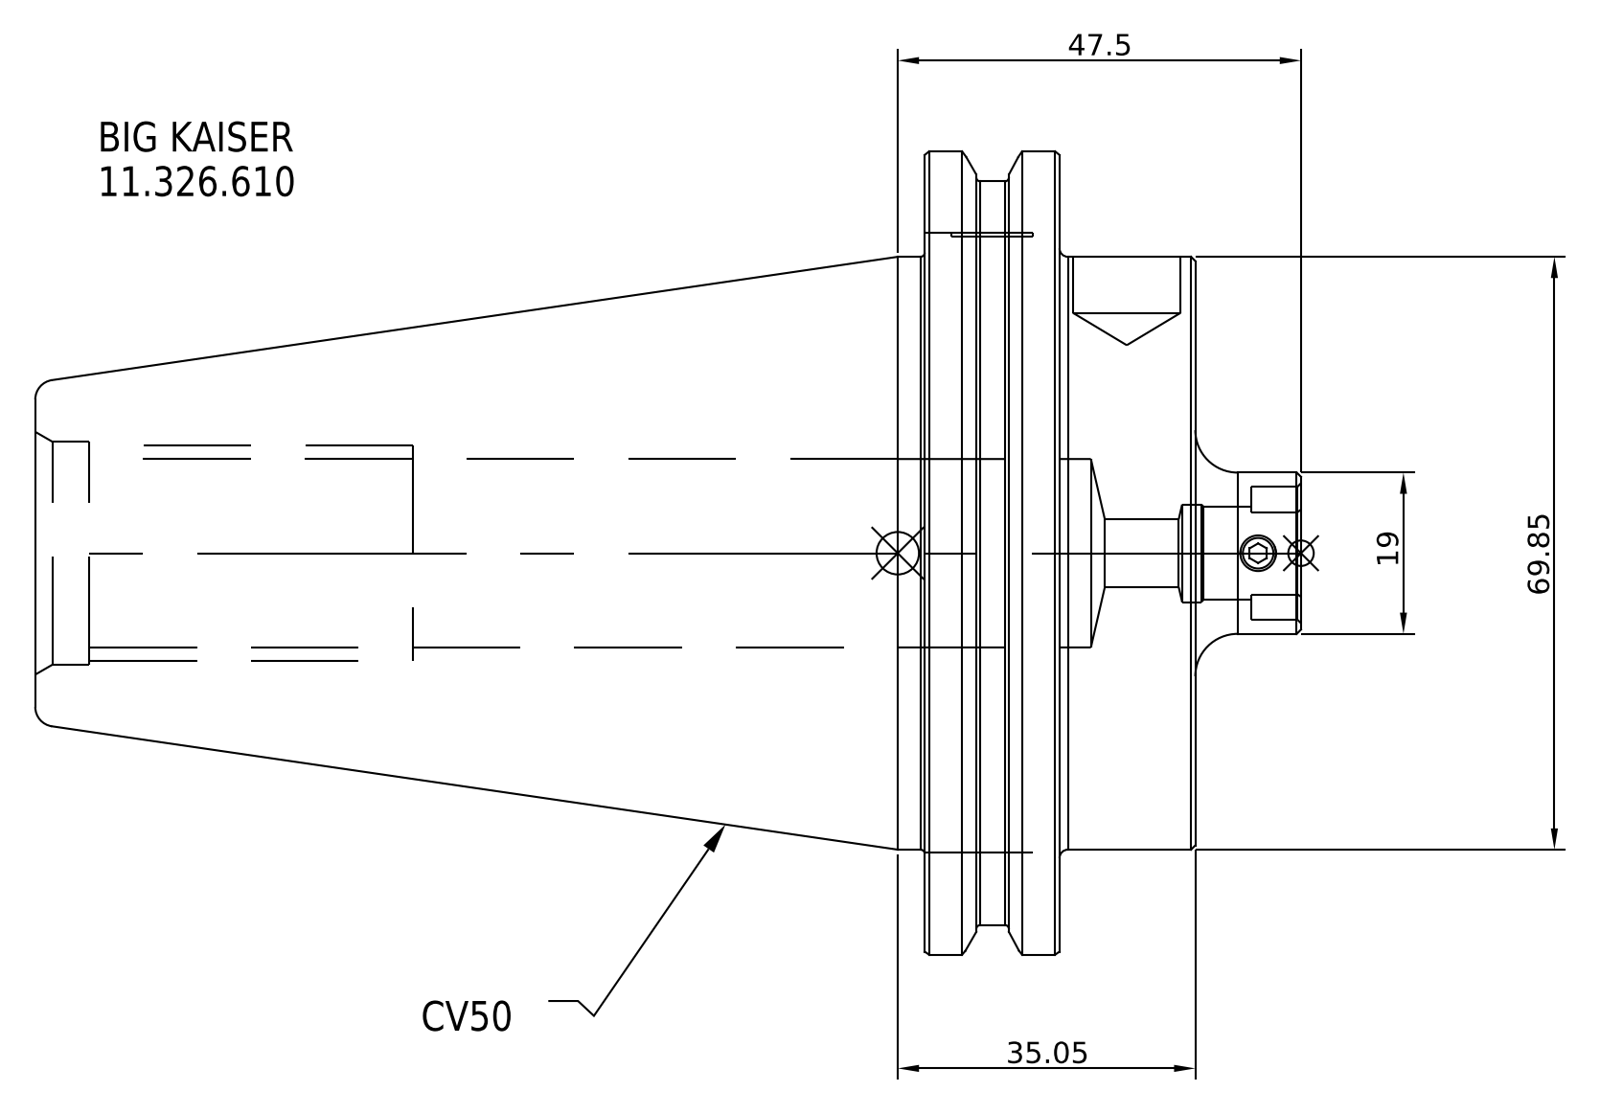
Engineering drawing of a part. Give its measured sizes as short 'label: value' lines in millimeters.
name: 11.326.610
written by: SolidWorks 2021 (CONFIG_CONTROL_DESIGN)
unit: mm
bodies: 1 solid, 16 faces (7 planar, 6 cylindrical, 3 other)
size: 149.1 × 98.43 × 98.43
volume: 446 043 mm³; area: 41 721 mm²
bosses: 1× ⌀98.43, 1× ⌀91.29, 1× ⌀69.85, 1× ⌀19.05
face distances: 17.55, 15.95, 33.5, 136.6, 120.65, 103.1, 12.5, 28.45, 46, 149.1
